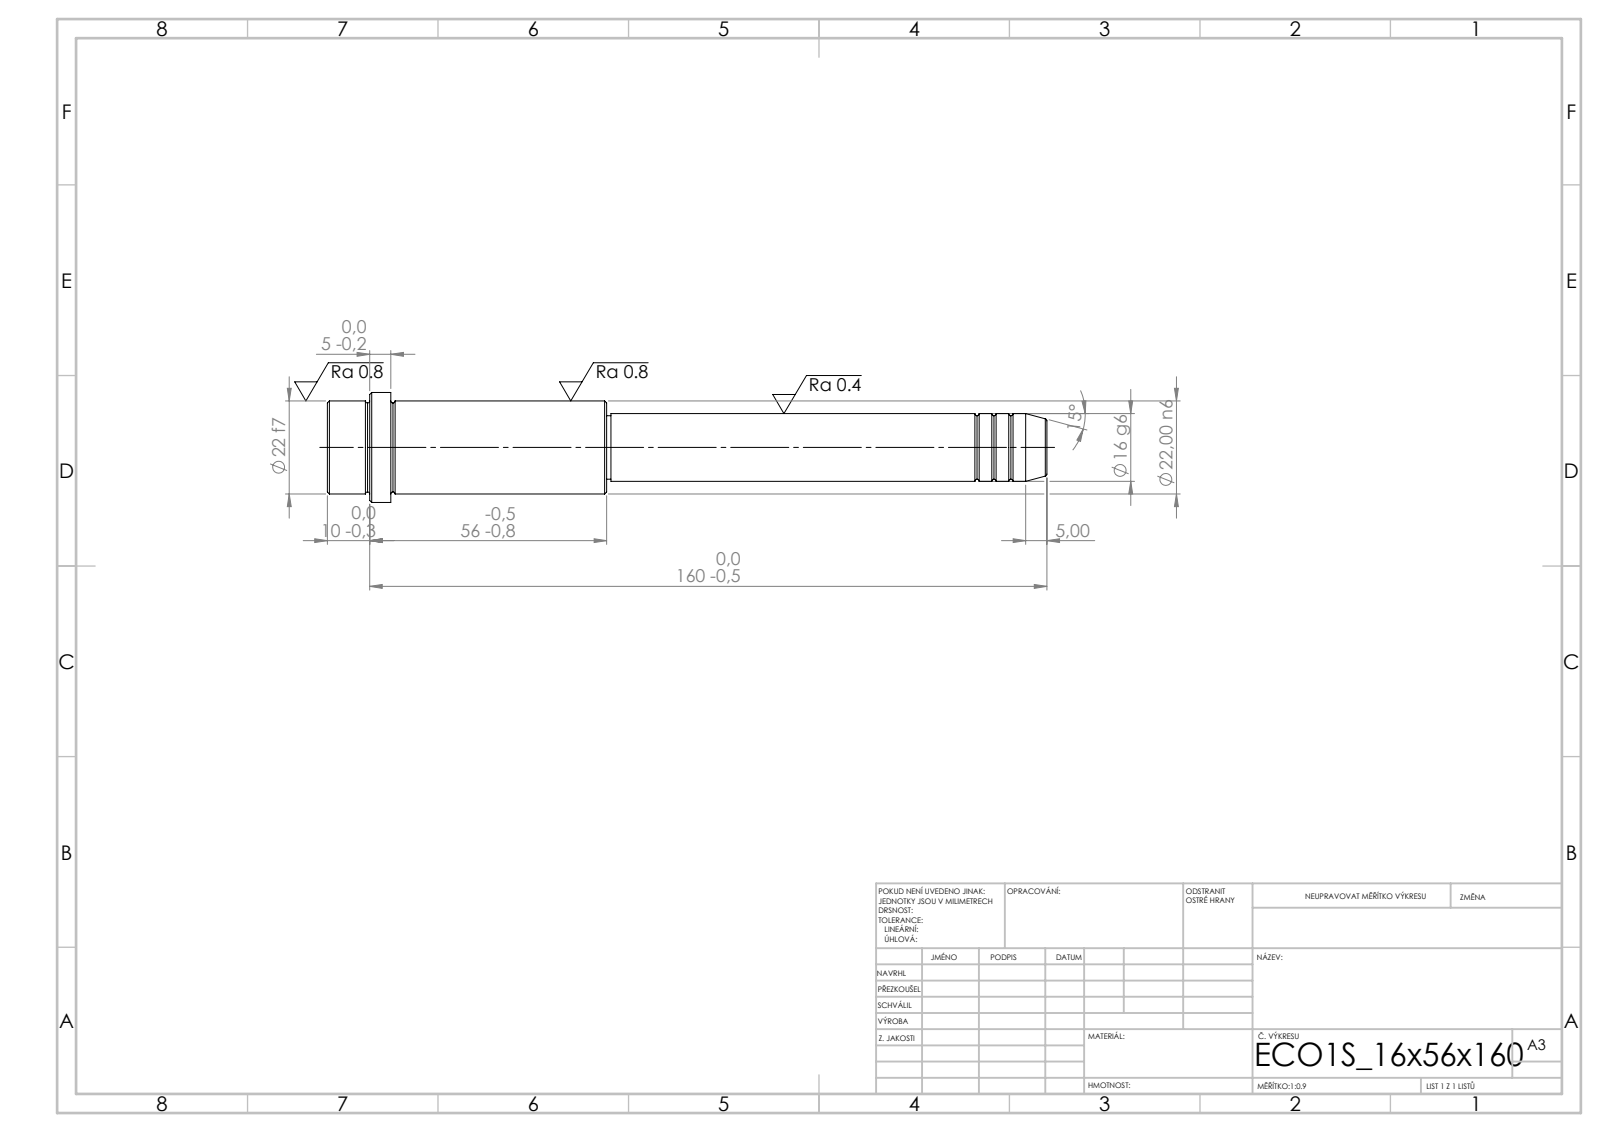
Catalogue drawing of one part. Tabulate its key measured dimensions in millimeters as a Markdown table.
| quantity | value |
| --- | --- |
| STEP written by | SolidWorks 2019 (CONFIG_CONTROL_DESIGN) |
| units | millimeters |
| bodies | 1 solid, 52 faces (6 planar, 16 cylindrical, 30 other) |
| overall size | 170 × 26 × 26 |
| volume | 46 431 mm³ |
| surface area | 10 964 mm² |
| round bosses / shafts (diameter × count) | 26 × 1, 22 × 1, 16 × 1, 15 × 1 |
| main face-to-face distances | 66, 51, 15, 104, 155, 170, 160, 56, 5, 10 |
